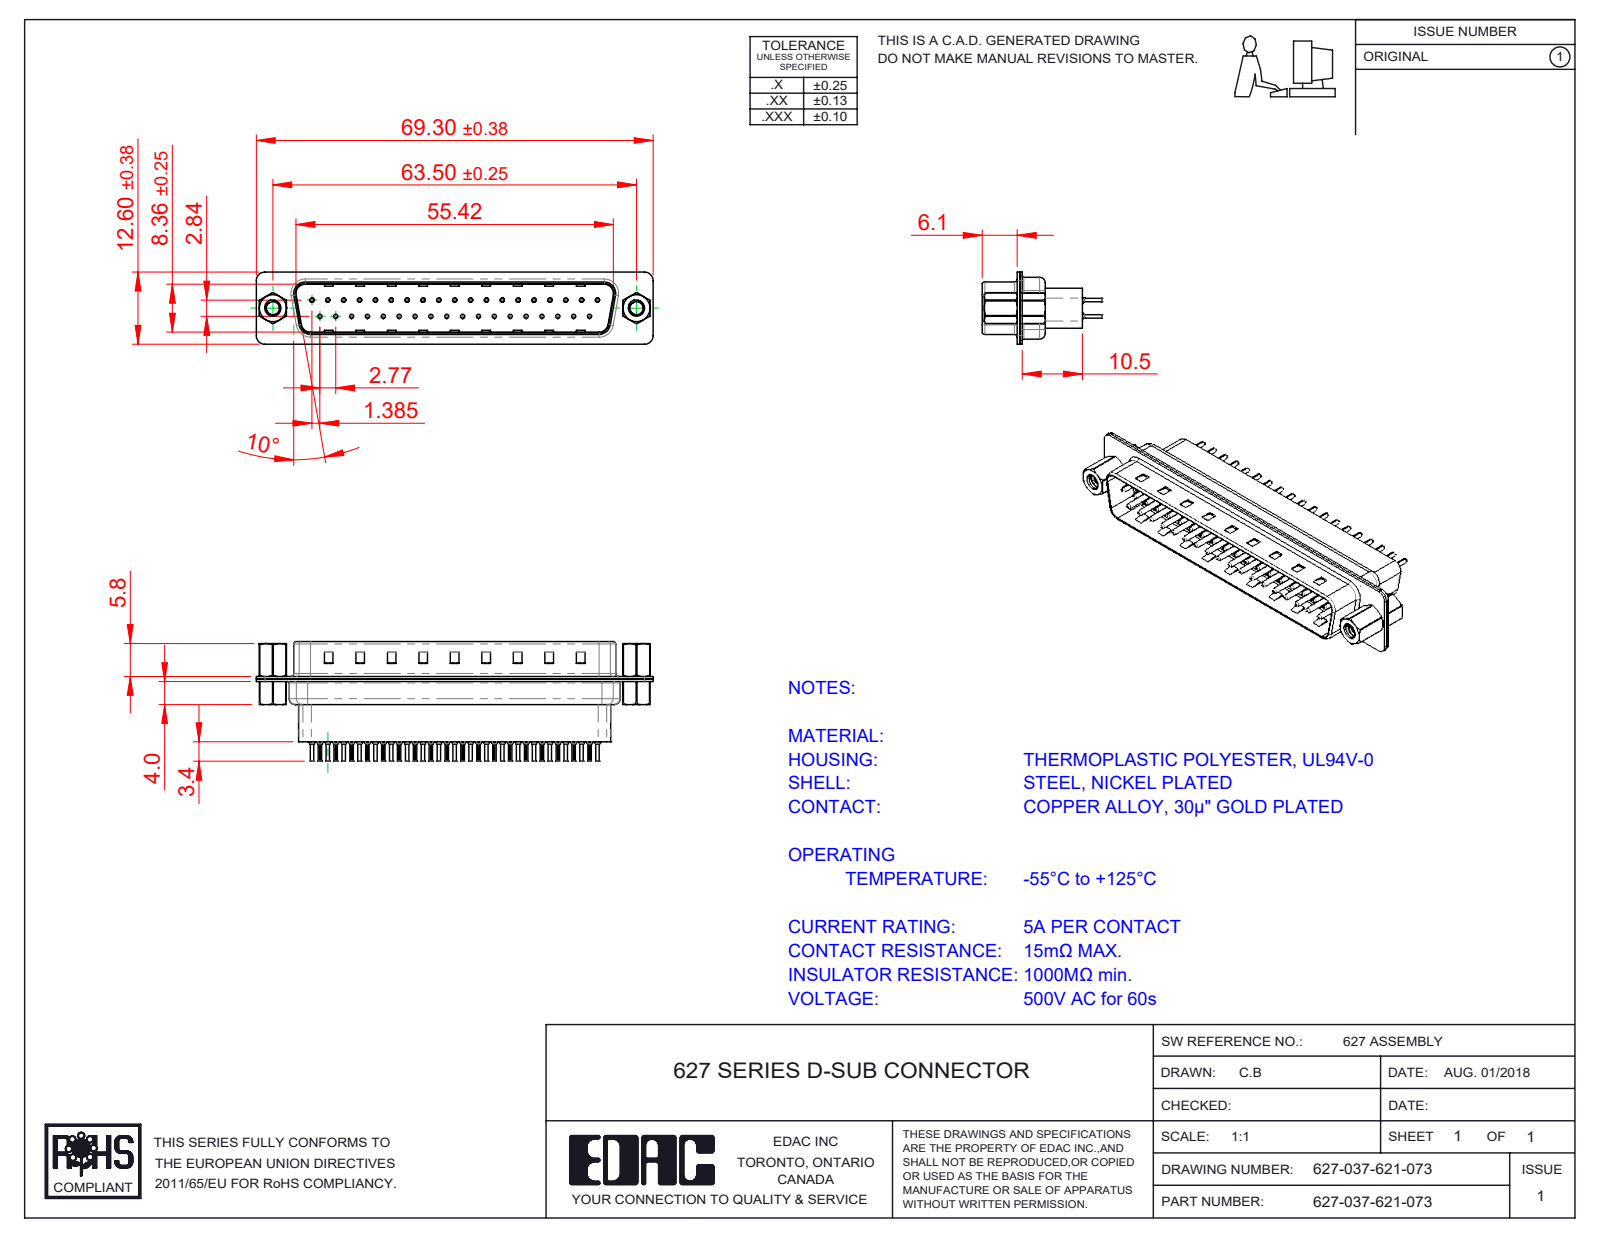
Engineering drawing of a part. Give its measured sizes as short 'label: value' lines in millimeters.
name: 627 Shell Rear_37 Contacts; 627 Shell Front_37 Contacts; 627 4-40 Hex Standoff; 627 Contact Row 1_21H (+4 more)
written by: SolidWorks 2020 (CONFIG_CONTROL_DESIGN)
unit: mm
bodies: 44 solids, 4160 faces (1113 planar, 1580 cylindrical, 1467 other)
size: 69.3 × 20.8 × 12.6
volume: 5 514 mm³; area: 14 032 mm²
holes: 37× ⌀0.2, 37× ⌀0.35, 37× ⌀1.1, 37× ⌀1.6, 2× ⌀2.26, 2× ⌀2.29, 2× ⌀4, 2× ⌀4.8
bosses: 37× ⌀2, 37× ⌀1.5, 37× ⌀0.75, 37× ⌀0.6, 2× ⌀5, 2× ⌀4.9, 2× ⌀2.79
rounds: 74× R0.1, 16× R1.5, 12× R2, 8× R0.5, 8× R1.6, 4× R0.25, 4× R0.6, 4× R0.65
face distances: 0.4, 0.82, 9.58, 0.45, 0.68, 7.68, 1.5, 1.08, 8.08, 8.76
hole spacings: 3.16, 2.77, 5.54, 8.31, 5.04, 10.1, 11.08, 12.78
